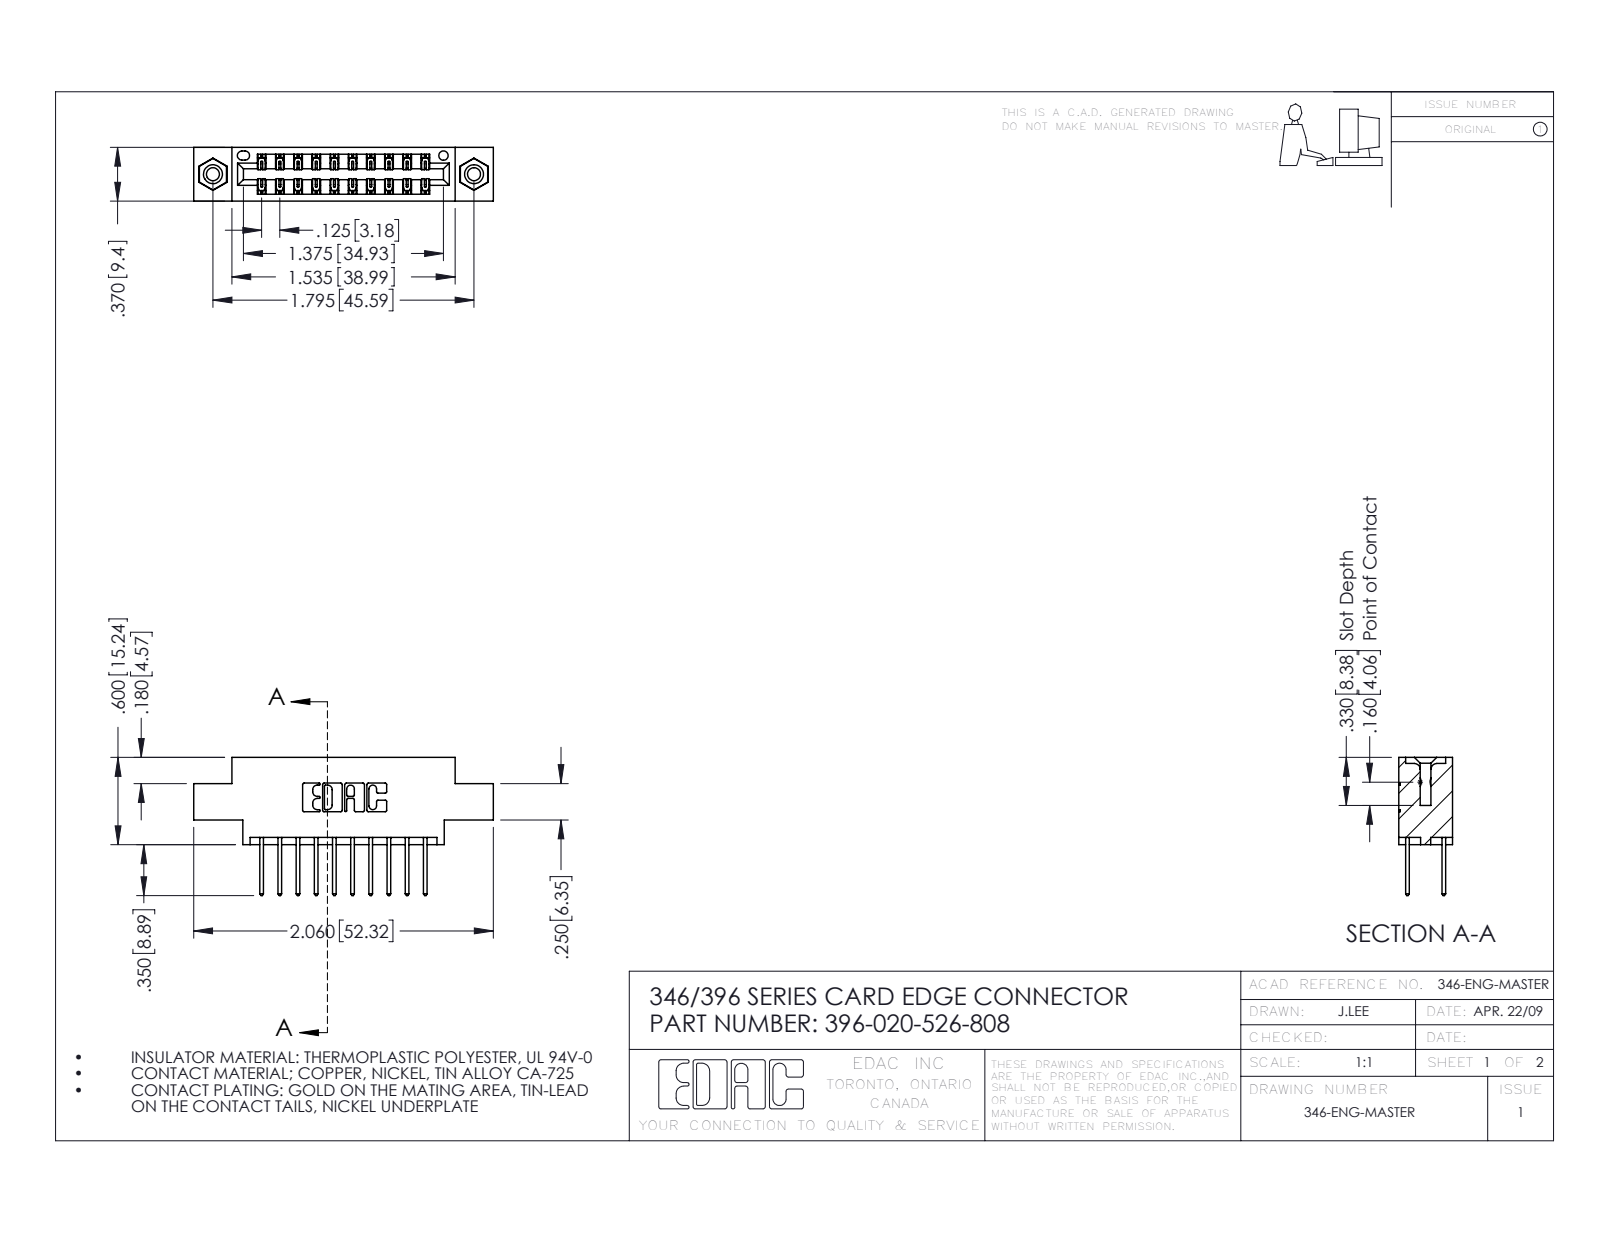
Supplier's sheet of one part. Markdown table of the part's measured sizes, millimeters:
| quantity | value |
| --- | --- |
| part name | 346 Part_0.170 Offset - 0.156 Dia-TI; 345-292-001_345-293-126; 396-020-526-808; 345-250-001_345-250-003-102 |
| STEP written by | SolidWorks 2016 (CONFIG_CONTROL_DESIGN) |
| units | millimeters |
| bodies | 23 solids, 1226 faces (812 planar, 398 cylindrical, 16 other) |
| overall size | 52.3 × 24.1 × 9.4 |
| volume | 4 720 mm³ |
| surface area | 6 339 mm² |
| round holes (diameter × count) | 2.3 × 2, 3.2 × 2, 4 × 2, 1.6 × 1 |
| round bosses / shafts (diameter × count) | 3.9 × 2 |
| partial cylindrical surfaces (radius × count) | 0.2 × 30, 0.3 × 22, 0.3 × 20, 0.2 × 6, 0.8 × 6, 0.7 × 3, 0.4 × 2, 0.6 × 2 |
| main face-to-face distances | 6.4, 1.2, 8.2, 9.4, 1.8, 7.6, 0.6, 7, 5.6, 3.8 |
| hole center spacings | 6.2, 40.4, 45.6 |
